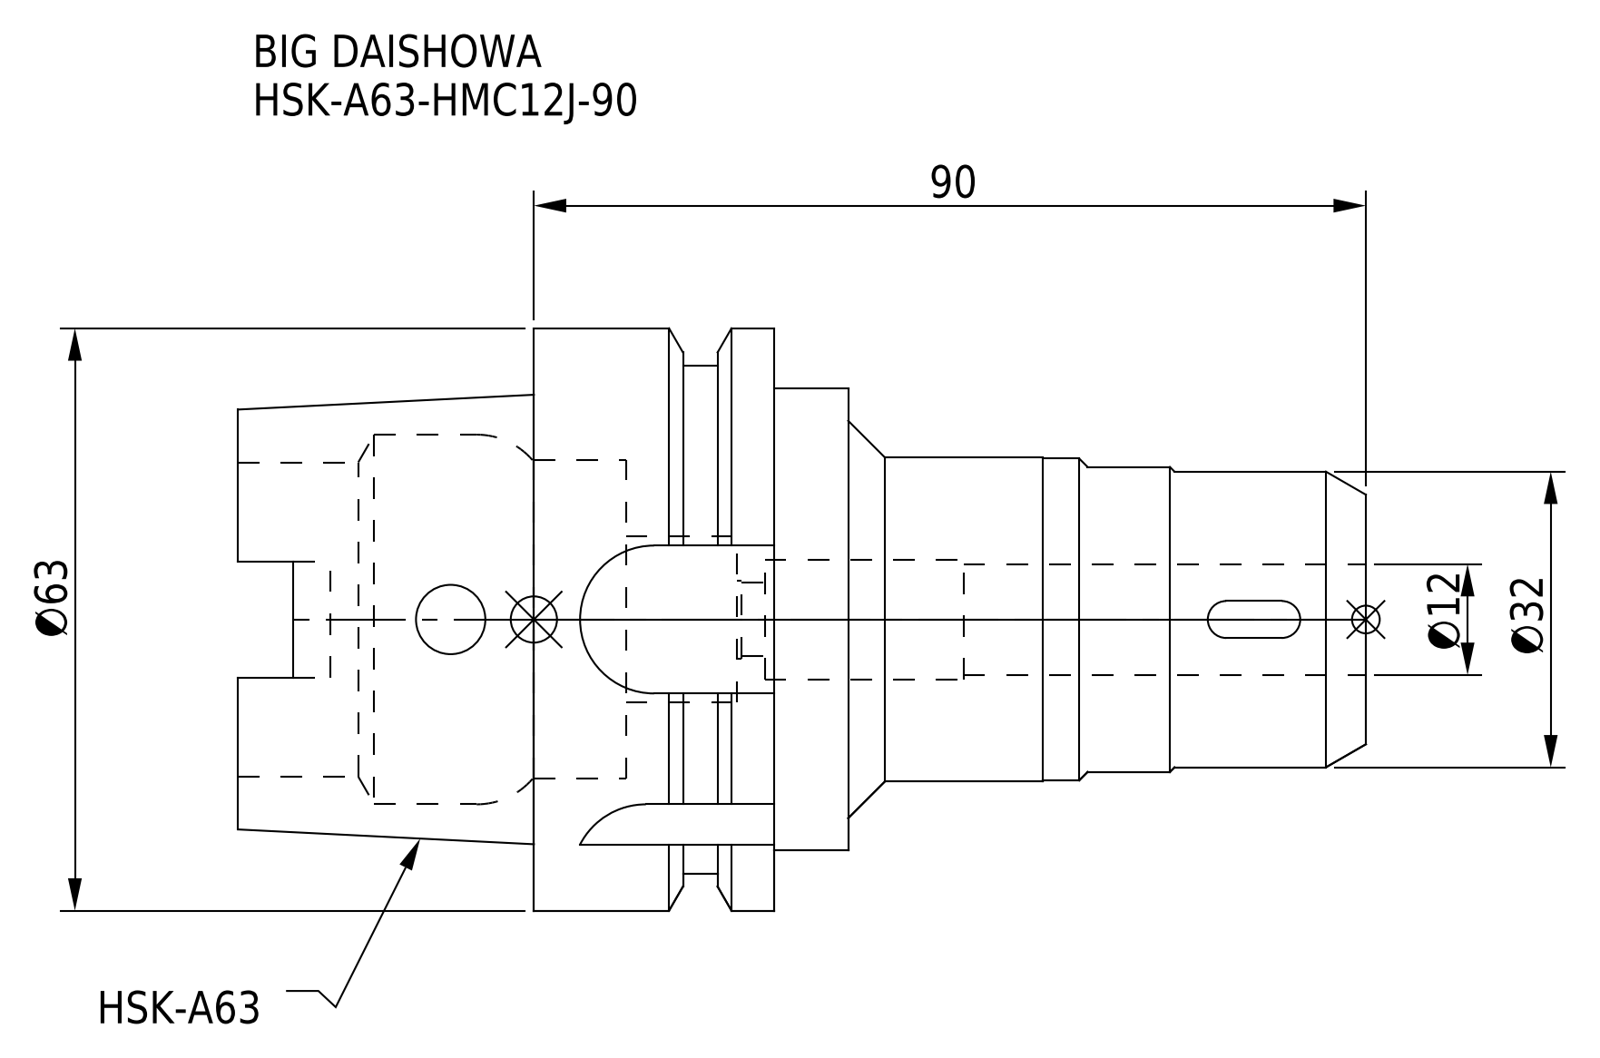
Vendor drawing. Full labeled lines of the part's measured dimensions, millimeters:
Part name (STEP PRODUCT): HSK-A63-HMC12J-90
STEP written by: CREO PARAMETRIC BY PTC INC, 2016380 (AUTOMOTIVE_DESIGN)
Units: millimetres
Bodies: 1 solid, 128 faces (53 planar, 55 cylindrical, 20 other)
Overall size (bounding box): 122 × 63 × 63
Volume: 139 345 mm³ · Surface area: 31 666 mm²
Round holes (diameter × count): ⌀7.5 ×1, ⌀8 ×1, ⌀8.4 ×1, ⌀12 ×1, ⌀13 ×1, ⌀18 ×1, ⌀34 ×1, ⌀34.5 ×1, ⌀40 ×1
Round bosses / shafts (diameter × count): ⌀63 ×1, ⌀55 ×1, ⌀50 ×1, ⌀35 ×1, ⌀34.8 ×1, ⌀33 ×1, ⌀32 ×1
Partial cylindrical surfaces — rounded edges, fillets, slot ends (radius × count): R2 ×4, R2.88 ×4, R8 ×4
Main face-to-face distances: 26, 16.05, 9.95, 58, 41.95, 32, 56, 8, 24.05, 34
